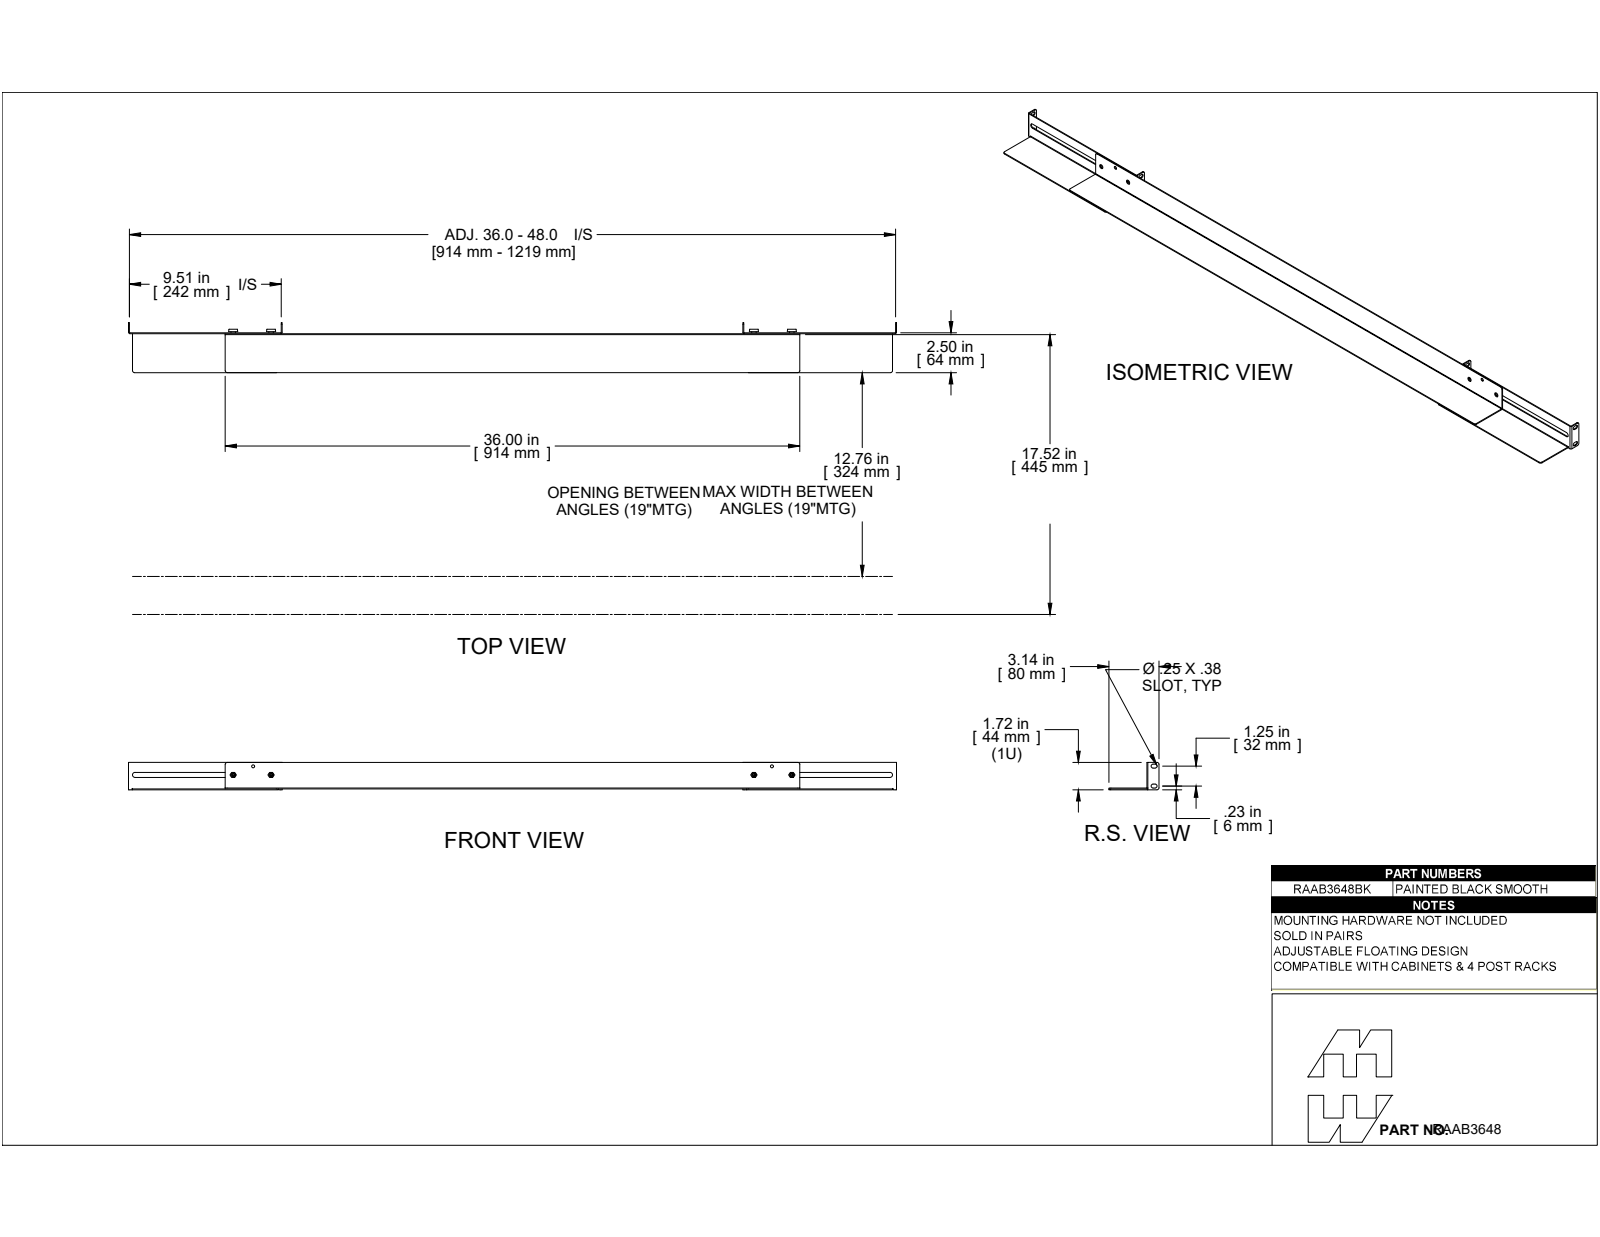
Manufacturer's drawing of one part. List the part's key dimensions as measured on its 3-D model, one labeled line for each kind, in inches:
Part name (STEP PRODUCT): RAAB3648BK
STEP written by: SolidWorks 2019 (AUTOMOTIVE_DESIGN)
Units: inches
Bodies: 15 solids, 312 faces (188 planar, 72 cylindrical, 52 other)
Overall size (bounding box): 48.114 × 3.143 × 1.718
Volume: 12.65 in³ · Surface area: 455.8 in²
Round holes (diameter × count): ⌀0.159 ×4, ⌀0.281 ×4, ⌀0.187 ×2
Round bosses / shafts (diameter × count): ⌀0.277 ×4, ⌀0.19 ×4, ⌀0.148 ×4
Partial cylindrical surfaces — rounded edges, fillets, slot ends (radius × count): R0.125 ×14, R0.029 ×6, R0.086 ×6, R0.157 ×4
Main face-to-face distances: 0.057, 0.114, 38.489, 9.568, 1.717, 1.66, 1.603, 2.38, 2.437, 2.494
Hole centre spacings: 1.36, 33.754, 1.246, 1.246, 2.375, 2.375, 30.25, 31.38
